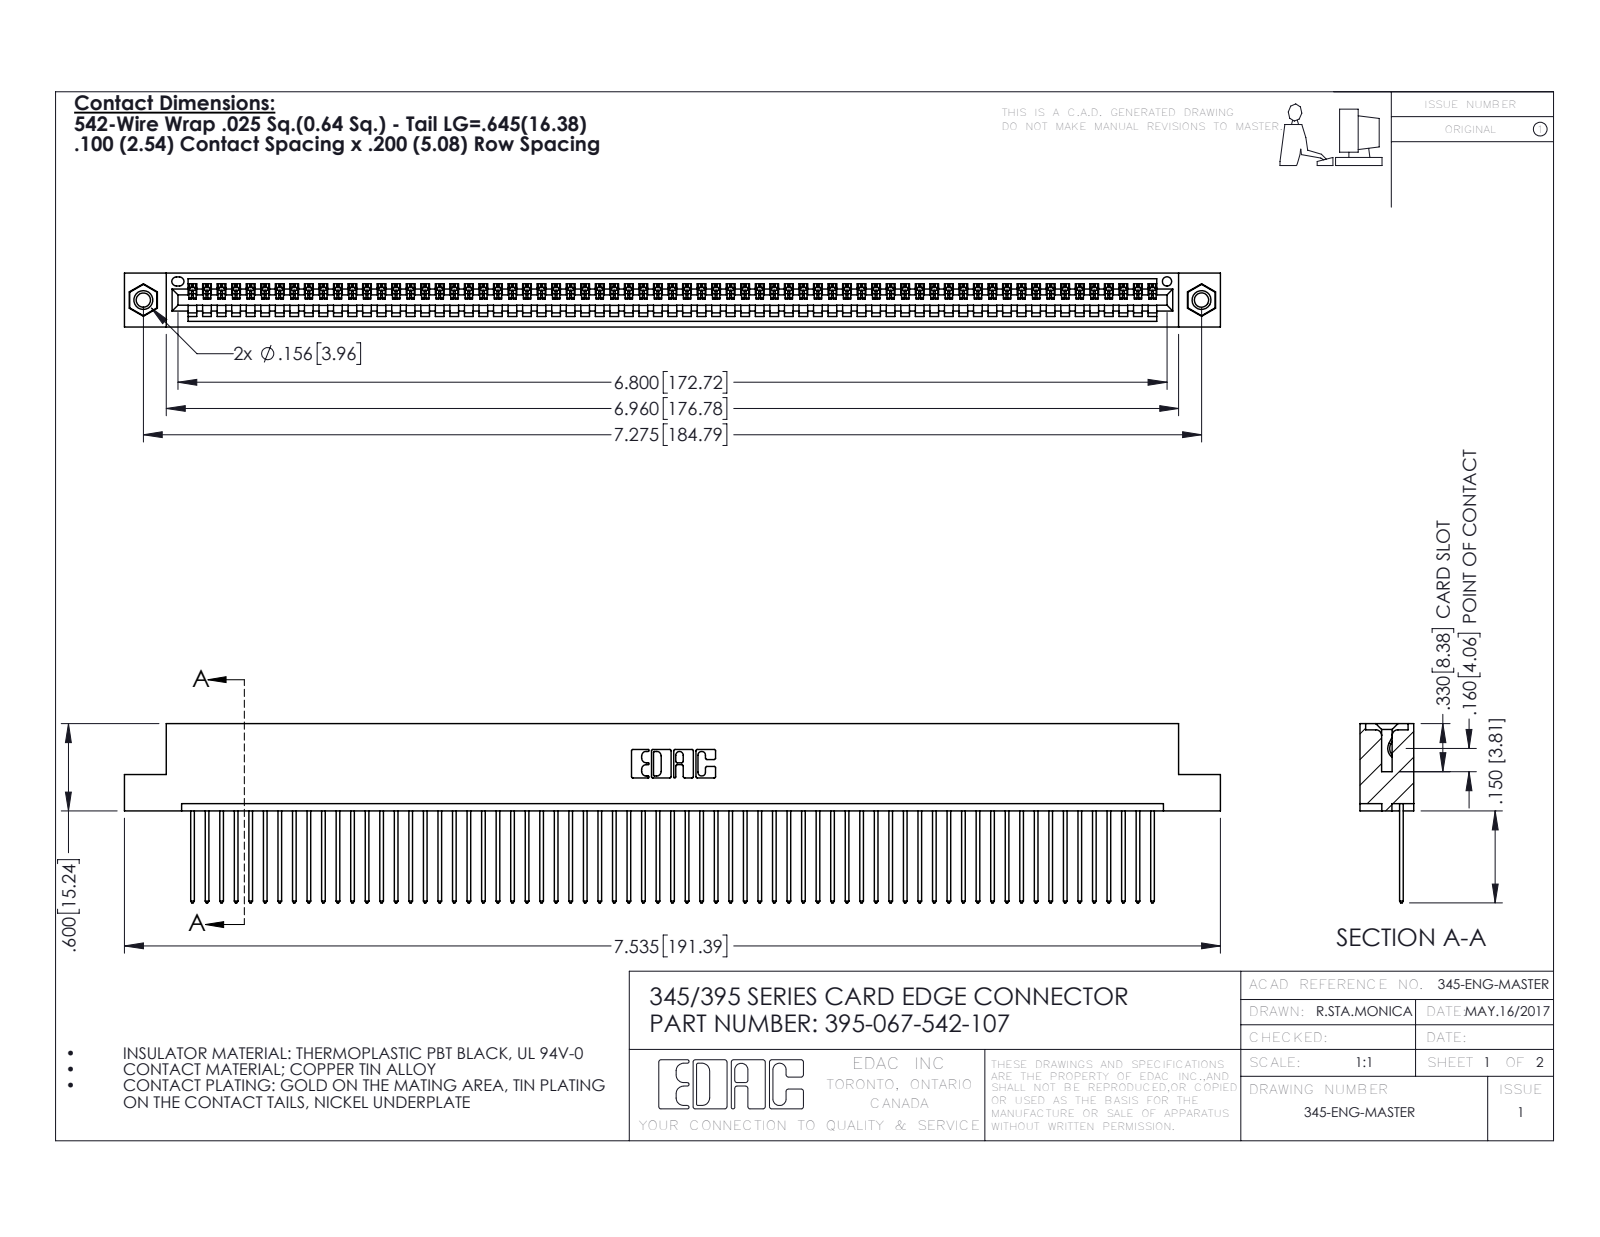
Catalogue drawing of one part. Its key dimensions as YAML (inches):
part_name: "345-250-001_345-250-005-103; 345 Part_Flush Mounting Lugs - 0.156 Dia-TI; 345-292-001_345-293-142; 395-067-542-107"
step_written_by: "SolidWorks 2016 (CONFIG_CONTROL_DESIGN)"
units: inches
bodies: {solids: 70, faces: 4072, planar: 2792, cylindrical: 1264, other: 16}
overall_size: [7.535, 1.232, 0.37]
volume: 1.13
surface_area: 40.18
round_holes:
  - {diameter: 0.098, count: 2}
  - {diameter: 0.125, count: 2}
  - {diameter: 0.156, count: 2}
  - {diameter: 0.064, count: 1}
round_bosses_or_shafts:
  - {diameter: 0.155, count: 2}
partial_cylinders:
  - {radius: 0.006, count: 134}
  - {radius: 0.01, count: 134}
  - {radius: 0.01, count: 22}
  - {radius: 0.007, count: 6}
  - {radius: 0.031, count: 6}
  - {radius: 0.026, count: 3}
  - {radius: 0.031, count: 2}
  - {radius: 0.04, count: 2}
face_to_face_distances: [0.072, 0.298, 0.098, 0.272, 0.025, 0.37, 0.2, 0.225, 0.149, 0.072]
hole_center_spacings: [0.27, 7.039, 7.275]
